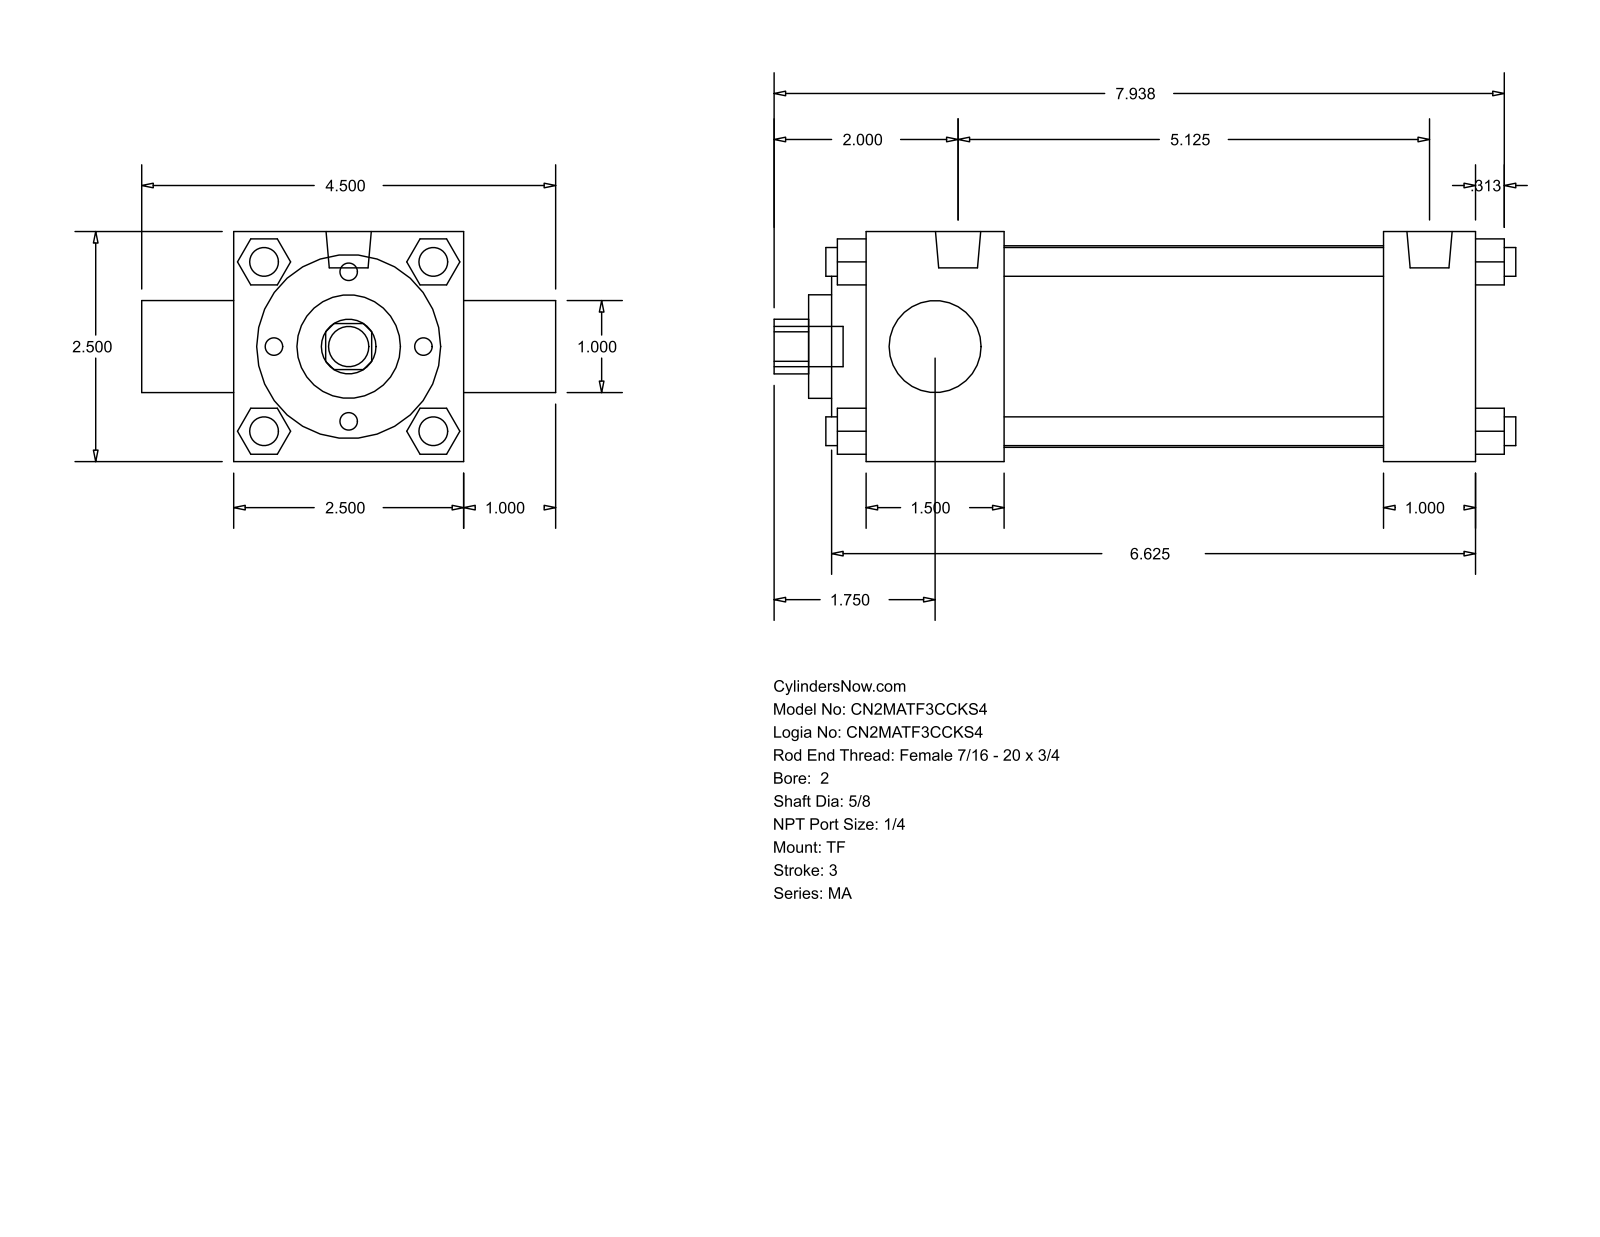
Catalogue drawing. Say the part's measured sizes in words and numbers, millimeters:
The part is named "MA_TF__0200_0.625". Its 3-D file was written by "GSSL Pune (CONFIG_CONTROL_DESIGN)". It is 0 solids with 122 faces: 93 planar, 29 cylindrical and 0 other. Overall it measures 204.79 by 114.3 by 63.5 millimeters. Round holes: 1 of diameter 15.88, 1 of diameter 25.4, 1 of diameter 28.57, 1 of diameter 50.8, 1 of diameter 55.63. Round bosses or shafts: 7 of diameter 7.94, 2 of diameter 12.49, 1 of diameter 11.11. Partial cylindrical surfaces (rounded edges, fillets, slot ends): 1 of radius 7.54. The main face-to-face distances are 63.5, 25.4, 38.1, 12.7, 168.28, 9.52, 142.88, 104.78, 130.18, 47.62.
